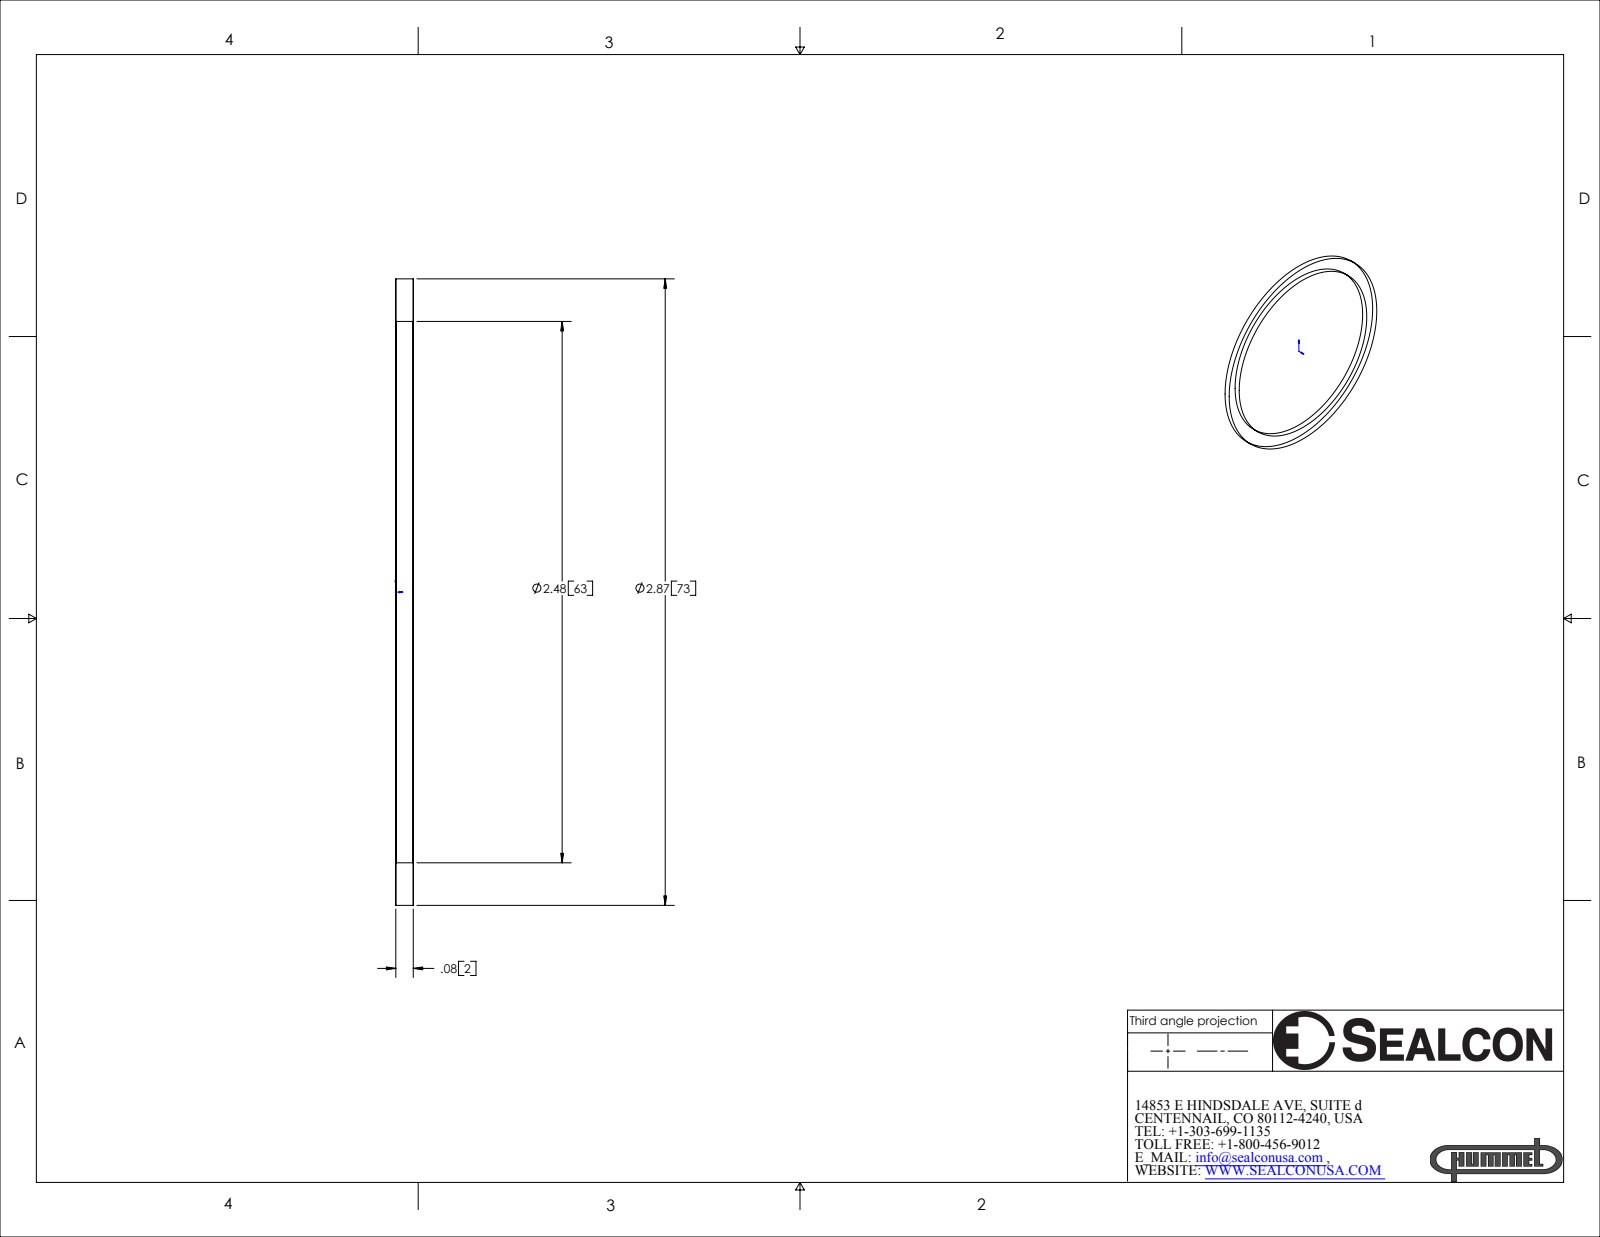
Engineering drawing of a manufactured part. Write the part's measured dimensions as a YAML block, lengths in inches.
part_name: "MS-63-NY"
step_written_by: "SolidWorks 2007 (CONFIG_CONTROL_DESIGN)"
units: inches
bodies: {solids: 1, faces: 6, planar: 2, cylindrical: 4, other: 0}
overall_size: [2.87, 2.87, 0.08]
volume: 0.131
surface_area: 4.622
round_holes:
  - {diameter: 2.48, count: 1}
round_bosses_or_shafts:
  - {diameter: 2.87, count: 1}
face_to_face_distances: [0.08]
